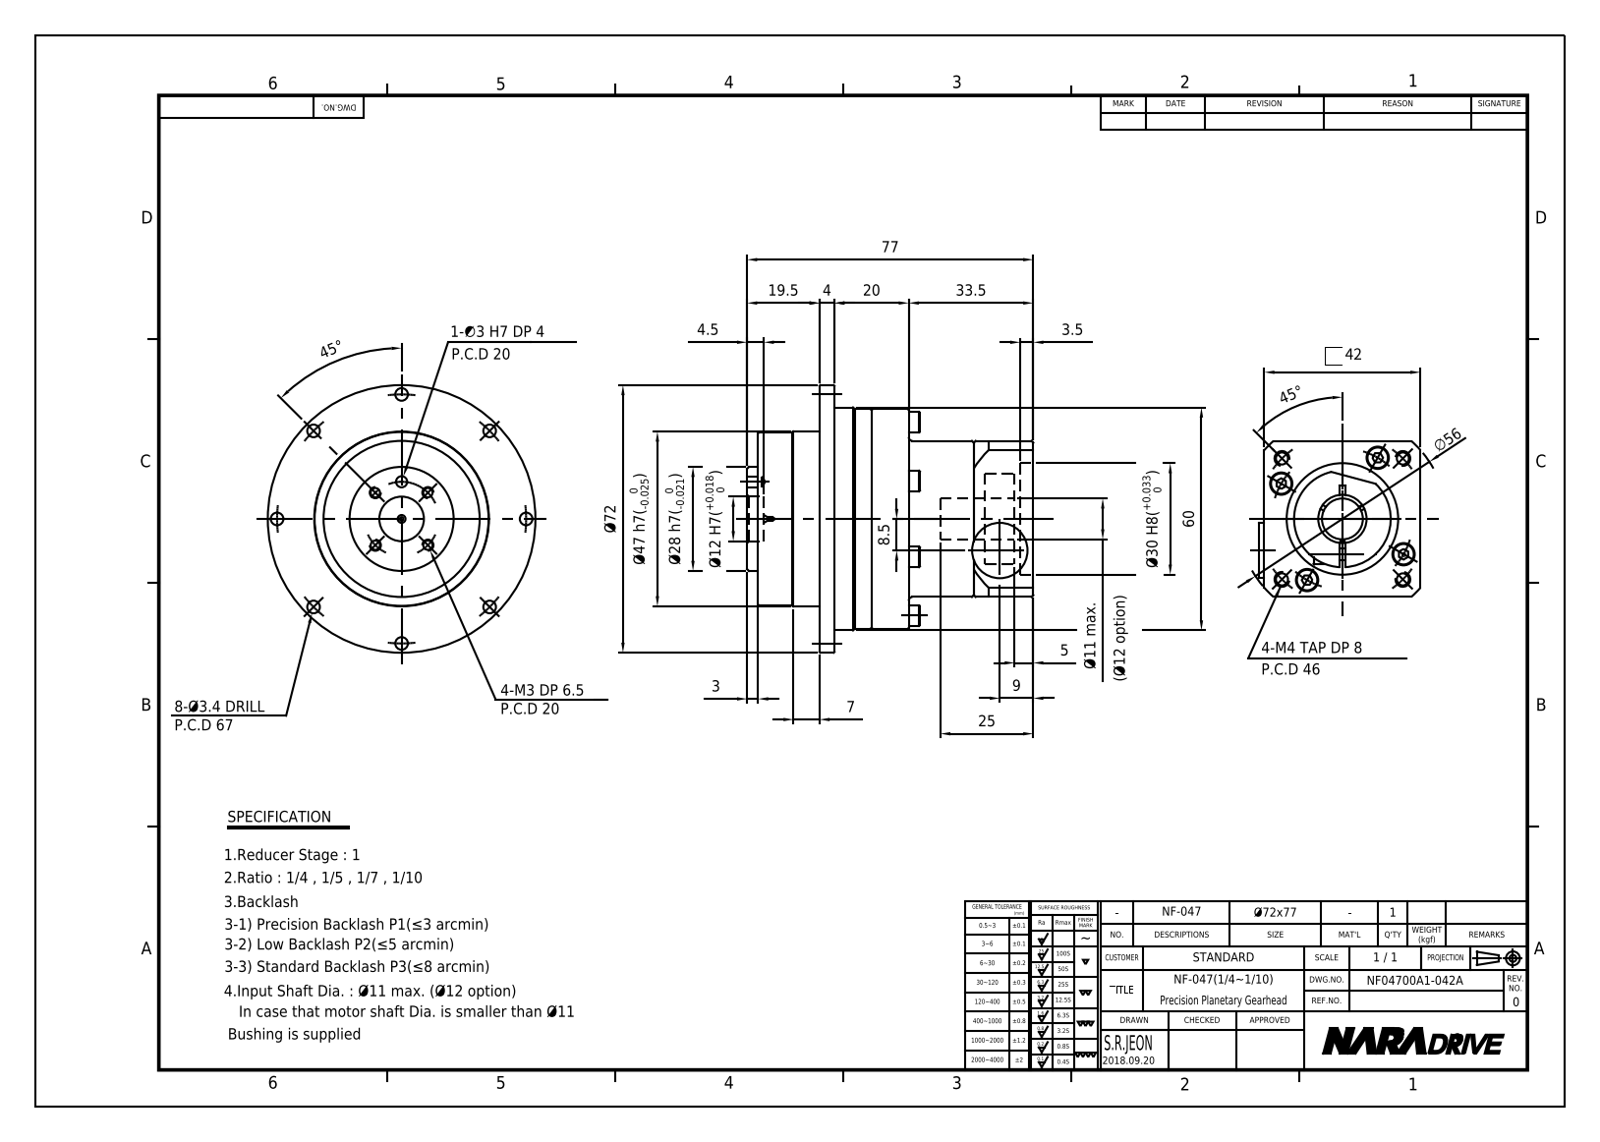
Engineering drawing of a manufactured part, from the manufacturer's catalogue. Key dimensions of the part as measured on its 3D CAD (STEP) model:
Part name (STEP PRODUCT): NF04700A1-042A
STEP written by: Autodesk Inventor 2015 (AUTOMOTIVE_DESIGN)
Units: millimetres
Bodies: 2 solids, 408 faces (198 planar, 103 cylindrical, 107 other)
Overall size (bounding box): 77 × 72 × 72
Volume: 119 706 mm³ · Surface area: 37 861 mm²
Round holes (diameter × count): ⌀3.4 ×21, ⌀2.46 ×13, ⌀3.24 ×4, ⌀6 ×4, ⌀1 ×1, ⌀3 ×1, ⌀7 ×1, ⌀8.5 ×1, ⌀11 ×1, ⌀12 ×1, ⌀13 ×1, ⌀28 ×1
Round bosses / shafts (diameter × count): ⌀5.5 ×13, ⌀3 ×13, ⌀72 ×1, ⌀60 ×1, ⌀59 ×1, ⌀47 ×1, ⌀46.5 ×1, ⌀42 ×1
Partial cylindrical surfaces — rounded edges, fillets, slot ends (radius × count): R3 ×1, R28 ×1
Main face-to-face distances: 10, 30.5, 20.5, 43.5, 33.5, 4, 40.5, 20, 24, 42
Hole centre spacings: 42.4, 23.8, 42.41, 7.5, 33.5, 36.77, 55.04, 55.05
